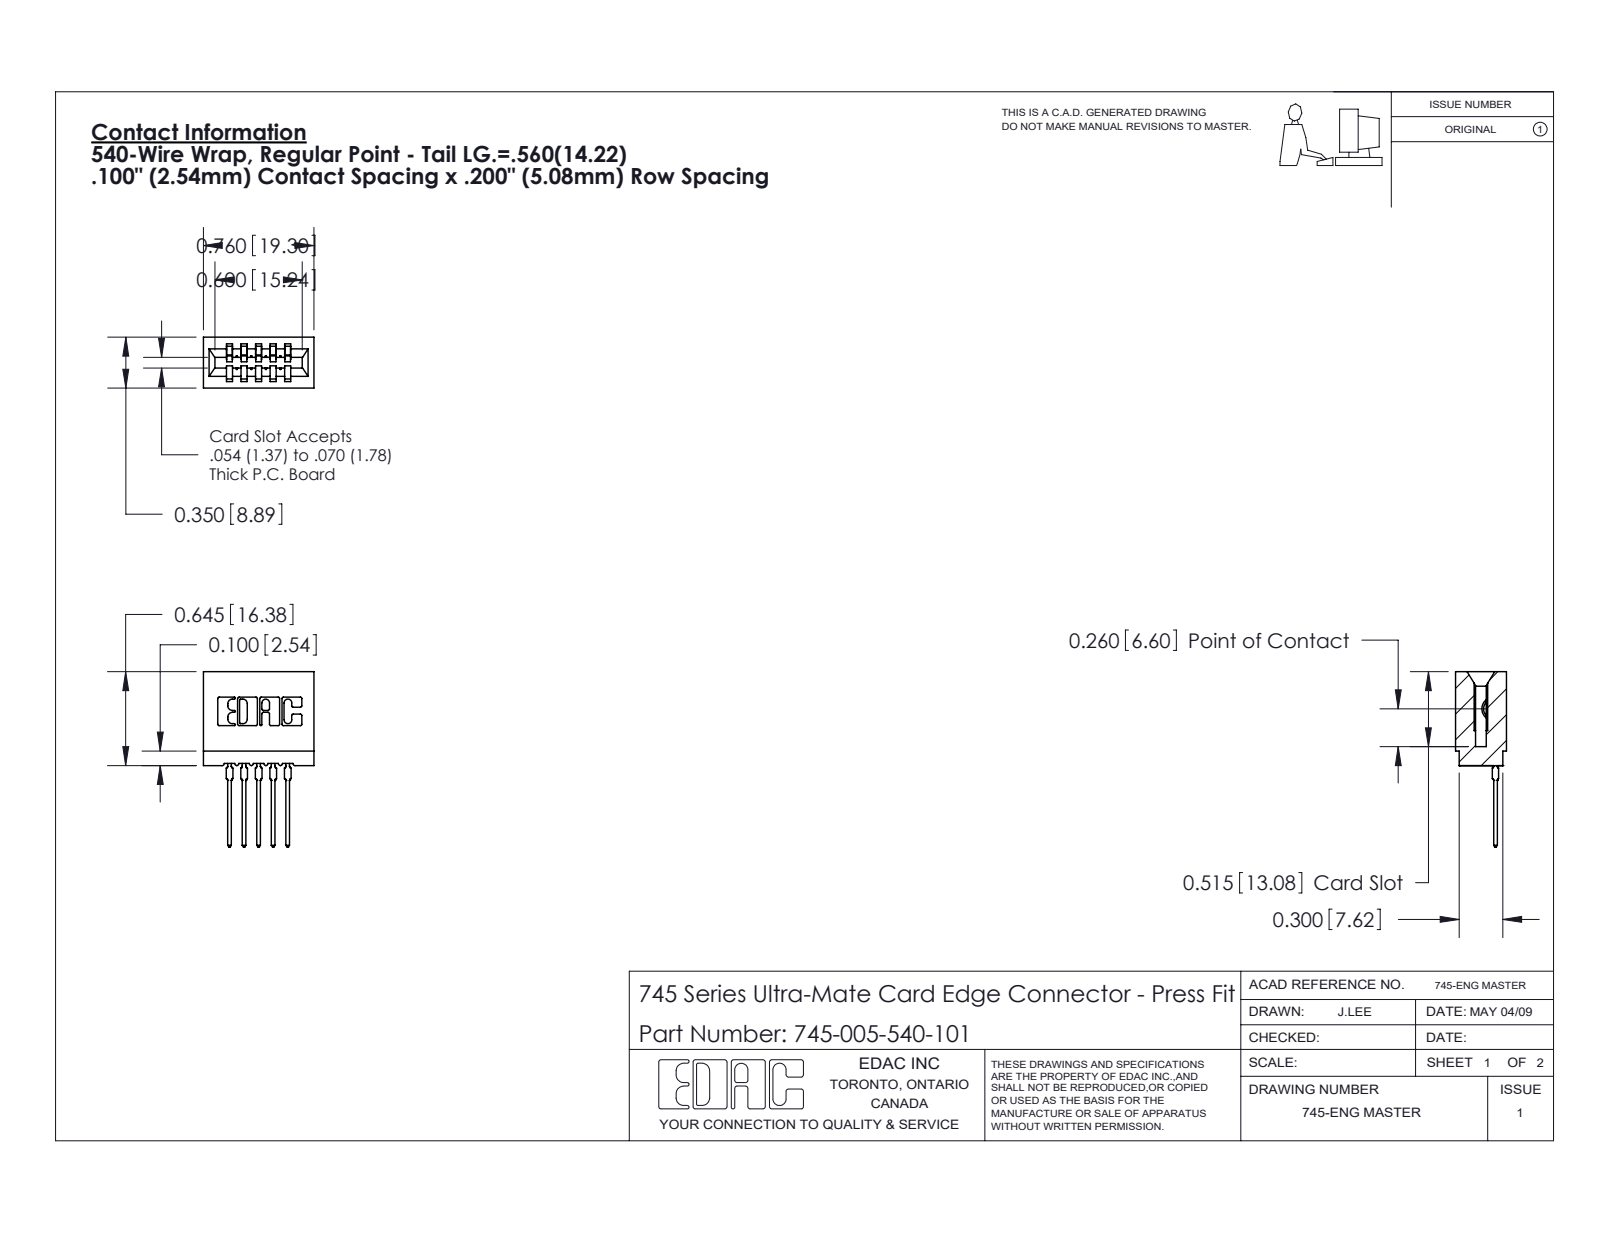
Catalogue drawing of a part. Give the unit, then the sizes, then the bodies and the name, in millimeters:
Units: millimetres
Overall size (bounding box): 30.6 × 19.3 × 8.9
Partial cylindrical surfaces — rounded edges, fillets, slot ends (radius × count): R0.3 ×22, R0.4 ×10, R0.5 ×10, R0.2 ×6, R0.8 ×6, R0.1 ×4, R0.3 ×4, R0.7 ×3
Main face-to-face distances: 2.5, 5.1, 1.1, 7.6, 3.6, 1.5, 8.9, 6.1, 4, 3.5
Volume: 1 930 mm³ · Surface area: 2 917 mm²
Bodies: 6 solids, 655 faces (390 planar, 135 cylindrical, 130 other)
Part name (STEP PRODUCT): 745 Part_Insulator Option - 01; 745-292-001_540; 745-005-540-101
STEP written by: SolidWorks 2020 (CONFIG_CONTROL_DESIGN)
